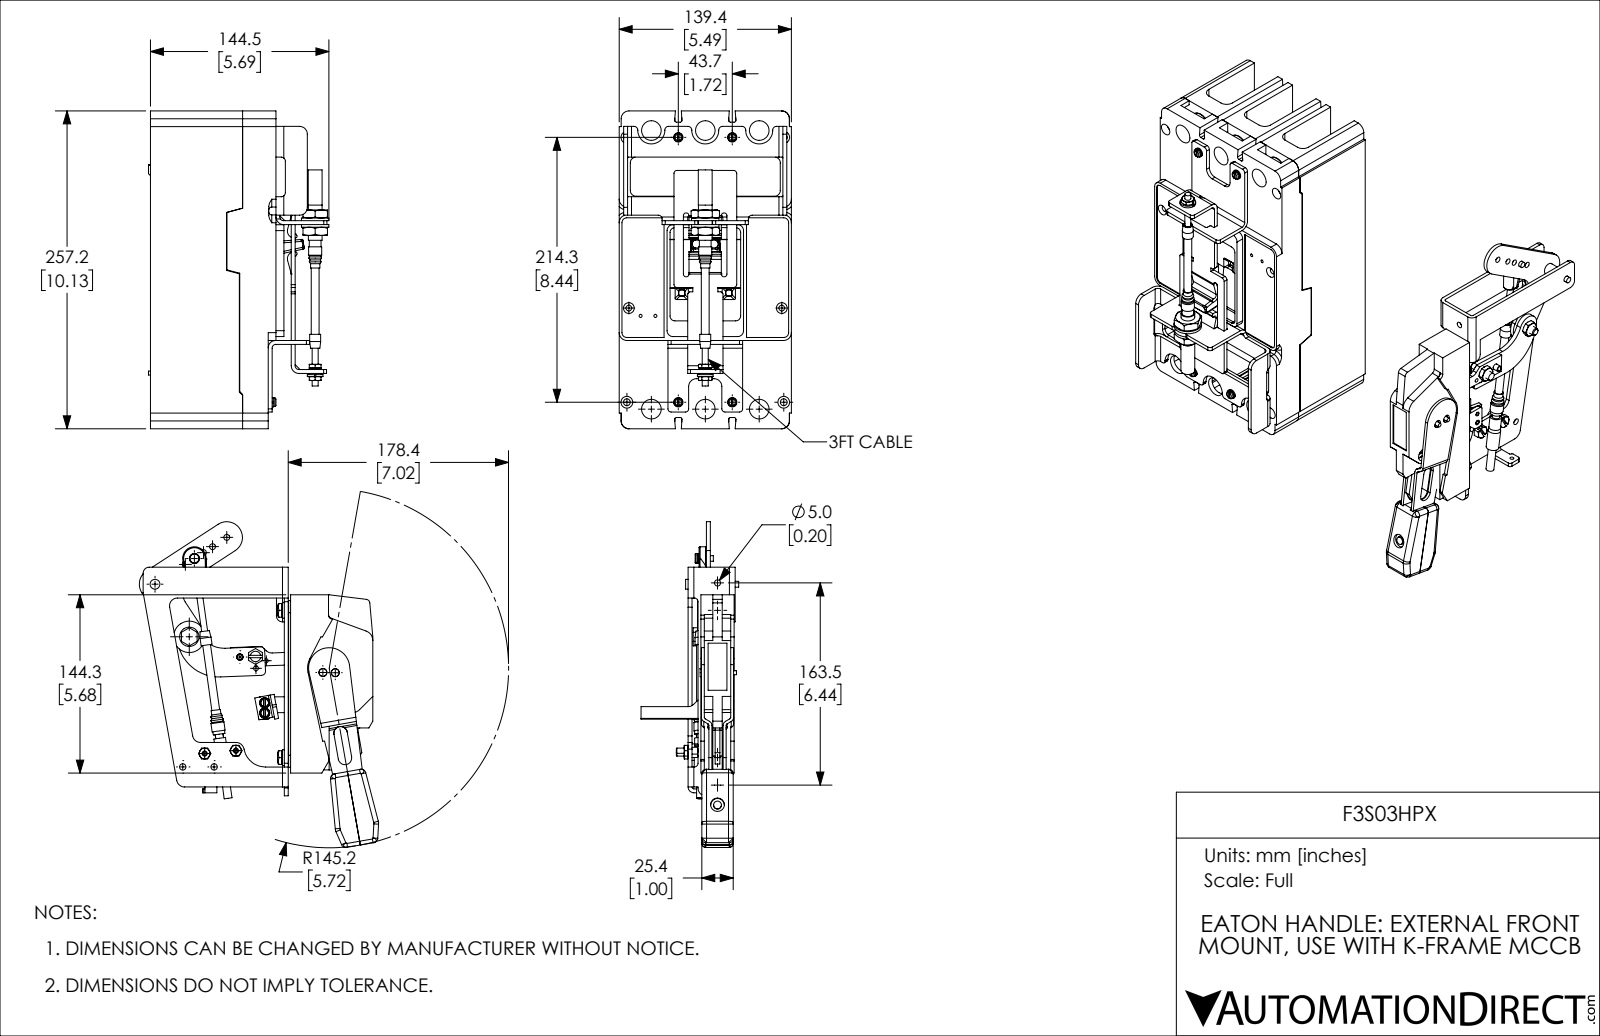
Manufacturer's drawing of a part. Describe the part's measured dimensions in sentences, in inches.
The part is named "F3S03HPX; F3S03HPX_HANDLE; F3S03HPX_BREAKER". Its 3-D file was written by "SolidWorks 2019 (CONFIG_CONTROL_DESIGN)". It is 81 solids with 2972 faces: 1428 planar, 1143 cylindrical and 401 other. Overall it measures 14.165 by 10.378 by 7.627 inches. Its volume is 182.3 cubic inches and its surface area 888.8 square inches. Round holes: 8 of diameter 0.219, 6 of diameter 0.203, 6 of diameter 0.228, 6 of diameter 0.625, 5 of diameter 0.188, 5 of diameter 0.196, 5 of diameter 0.281, 5 of diameter 0.375, 5 of diameter 0.438, 4 of diameter 0.168, 4 of diameter 0.25, 4 of diameter 0.5. Round bosses or shafts: 9 of diameter 0.25, 6 of diameter 0.338, 5 of diameter 0.375, 4 of diameter 0.5, 4 of diameter 0.297, 4 of diameter 0.27, 4 of diameter 0.138, 3 of diameter 0.394. Partial cylindrical surfaces (rounded edges, fillets, slot ends): 109 of radius 0.062, 53 of radius 0.125, 50 of radius 0.25, 22 of radius 0.032, 18 of radius 0.156, 16 of radius 0.1, 16 of radius 0.188, 15 of radius 0.031. The main face-to-face distances are 0.125, 5.49, 0.249, 2.906, 1.062, 3.719, 0.813, 0.032, 4, 0.156. The hole center spacings are 1.719, 8.17, 7.907, 8.7, 9.04, 0.531, 1.141, 1.141.
